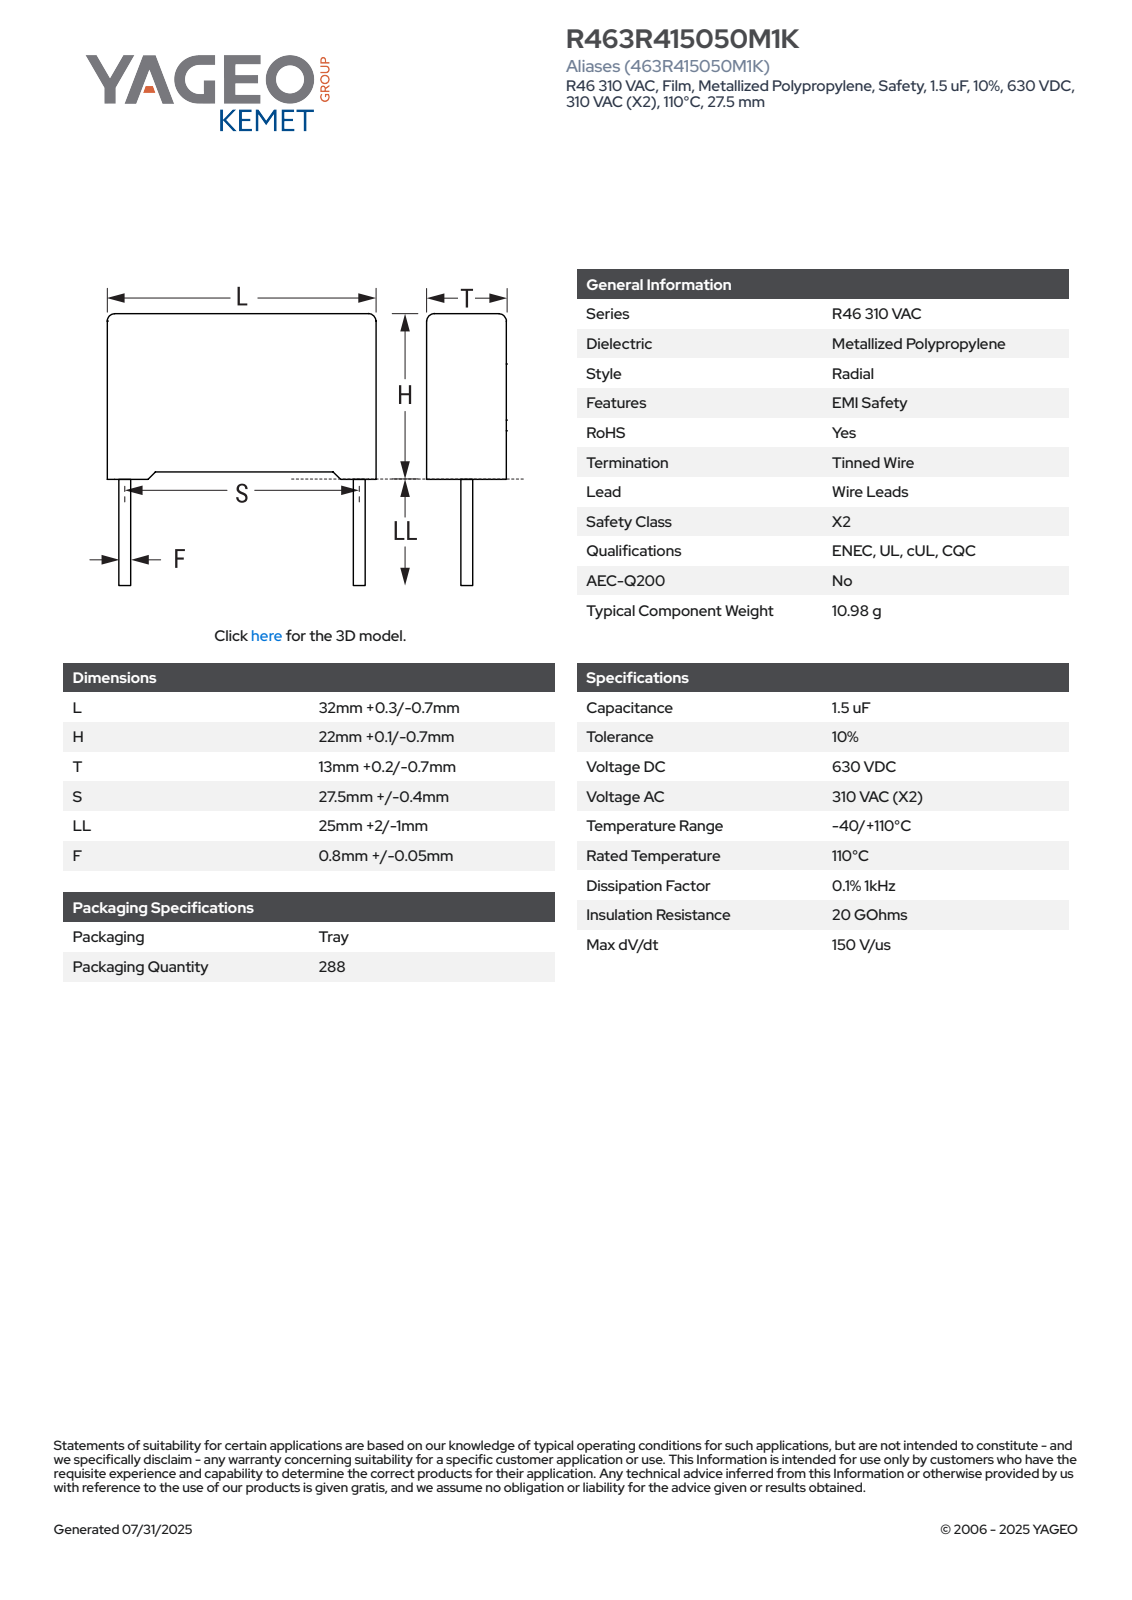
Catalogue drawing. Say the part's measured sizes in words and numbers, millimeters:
The part is named "CFR_RB2_32X22X13_L32.3H22.1T13.2S27.5LL27F0.85". Its 3-D file was written by "SolidWorks 2021 (AUTOMOTIVE_DESIGN)". It is 4 solids with 85 faces: 77 planar, 8 cylindrical and 0 other. Overall it measures 49.1 by 32.3 by 13.21 millimeters. Its volume is 9 158 cubic millimeters and its surface area 3 062 square millimeters. Round bosses or shafts: 2 of diameter 0.85. Partial cylindrical surfaces (rounded edges, fillets, slot ends): 4 of radius 0.5. The main face-to-face distances are 13.2, 21.34, 32.3, 21.35, 0.75, 0.76, 22.1, 1.08, 13.21, 31.22.
